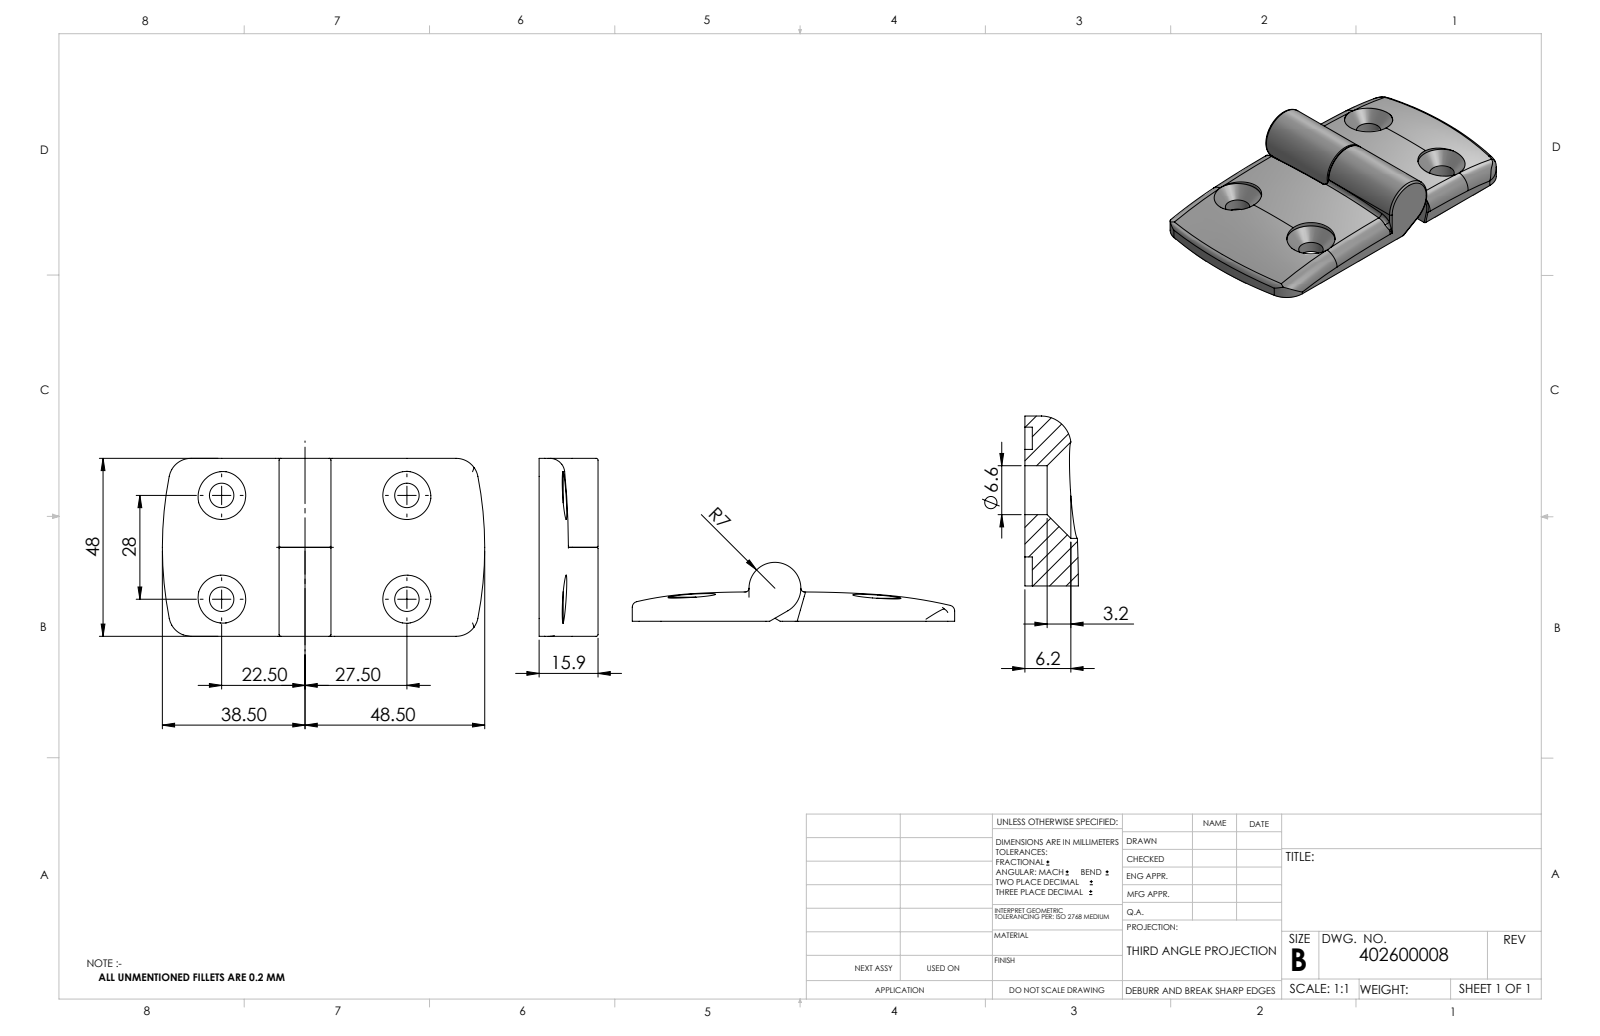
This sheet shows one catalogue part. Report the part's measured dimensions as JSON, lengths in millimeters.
{"part_name": "402600008_c_1", "step_written_by": "SolidWorks 2014 (CONFIG_CONTROL_DESIGN)", "units": "millimeters", "bodies": {"solids": 3, "faces": 189, "planar": 80, "cylindrical": 49, "other": 60}, "overall_size": [87, 48, 16.16], "volume_mm3": 26979, "surface_area_mm2": 13434, "round_holes": [[6.6, 4], [6, 1]], "round_bosses_or_shafts": [[14, 1], [6.2, 1]], "partial_cylinders_radius": [[0.3, 6], [0.5, 6], [6, 4], [6.5, 4], [4, 2], [100, 2]], "face_to_face_distances": [1, 24, 1.5, 2, 5, 3, 48, 0.5, 22, 17], "hole_center_spacings": [28, 50, 57.31]}
